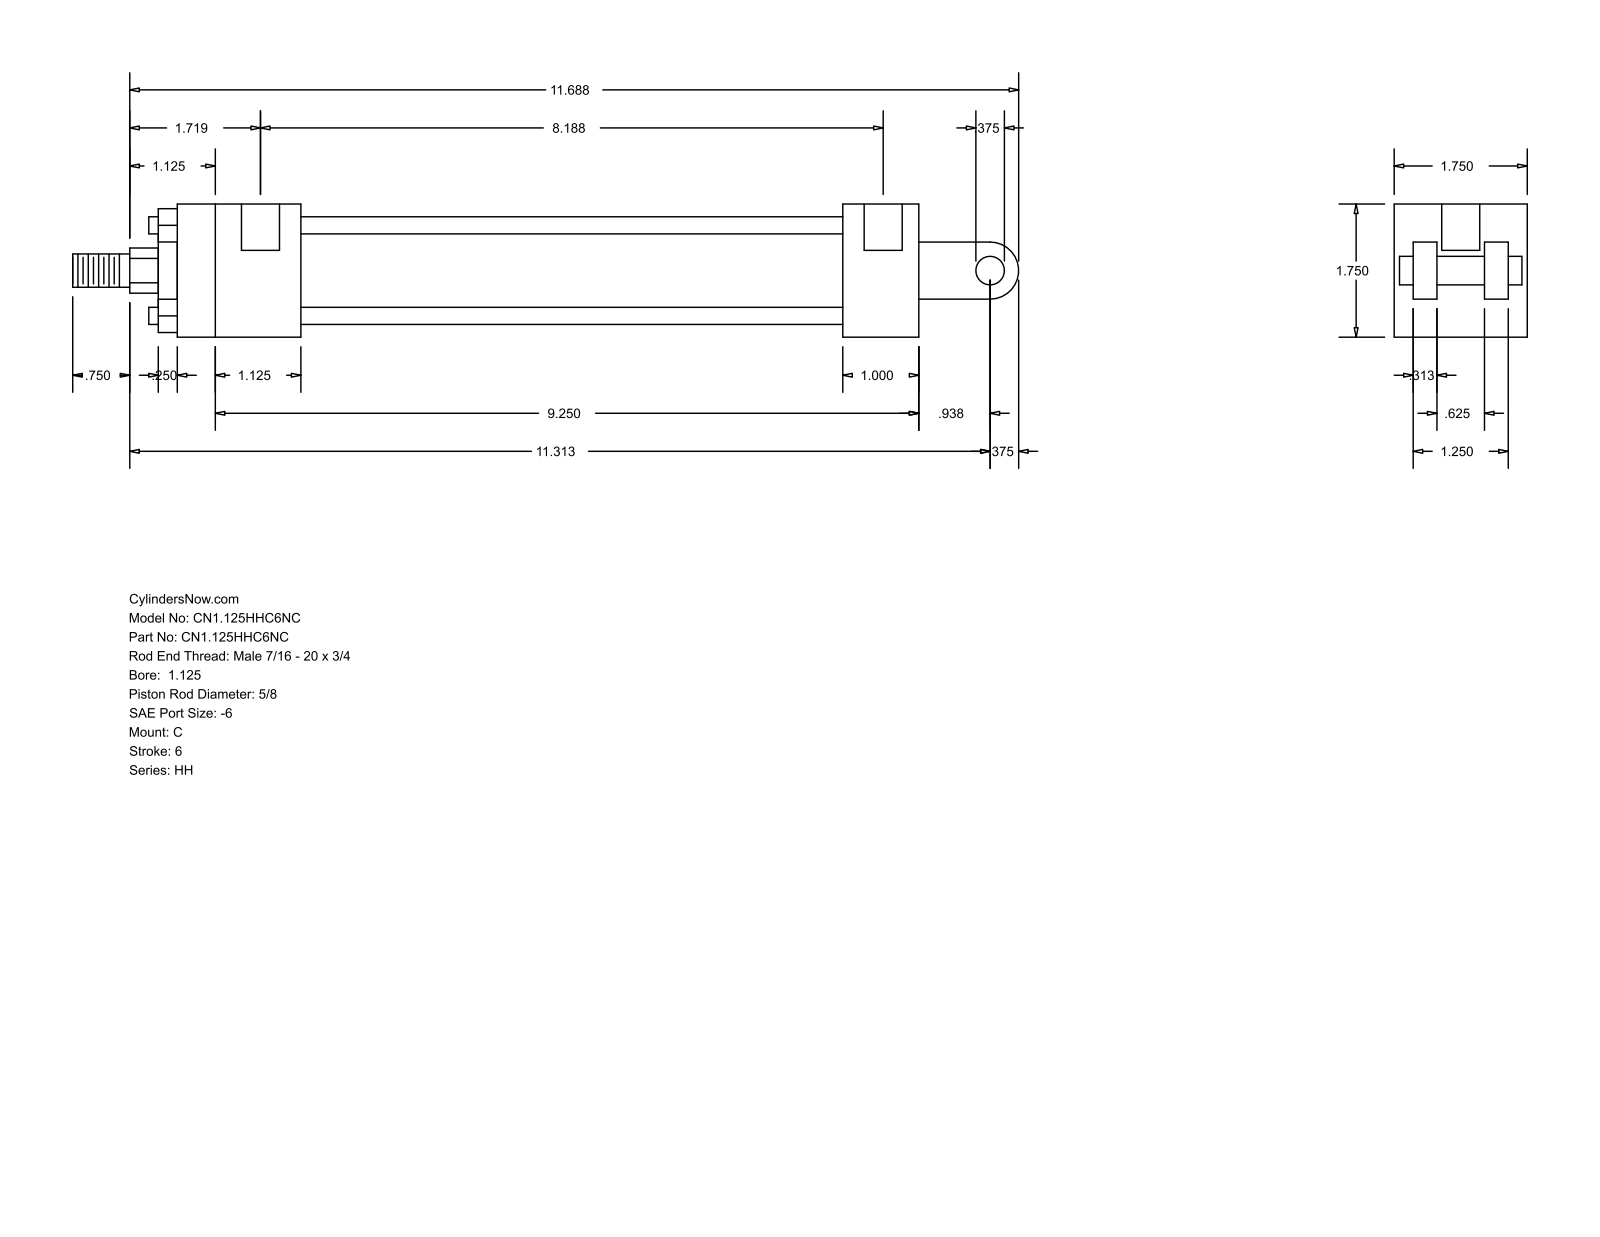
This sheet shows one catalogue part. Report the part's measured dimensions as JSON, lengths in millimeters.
{"part_name": "HH_C__0112_0.625", "step_written_by": "GSSL Pune (CONFIG_CONTROL_DESIGN)", "units": "millimeters", "bodies": {"solids": 0, "faces": 99, "planar": 70, "cylindrical": 29, "other": 0}, "overall_size": [315.91, 44.45, 44.45], "round_holes": [[5.56, 4], [12.7, 2]], "round_bosses_or_shafts": [[5.71, 4], [34.92, 1], [28.57, 1], [15.88, 1], [11.11, 1], [9.53, 1]], "partial_cylinders_radius": [[7.54, 1], [9.53, 1]], "face_to_face_distances": [44.46, 6.35, 31.76, 14.29, 25.4, 30.17, 38.11, 7.94, 23.82, 41.27], "hole_center_spacings": [204.79, 3.17, 207.96]}
